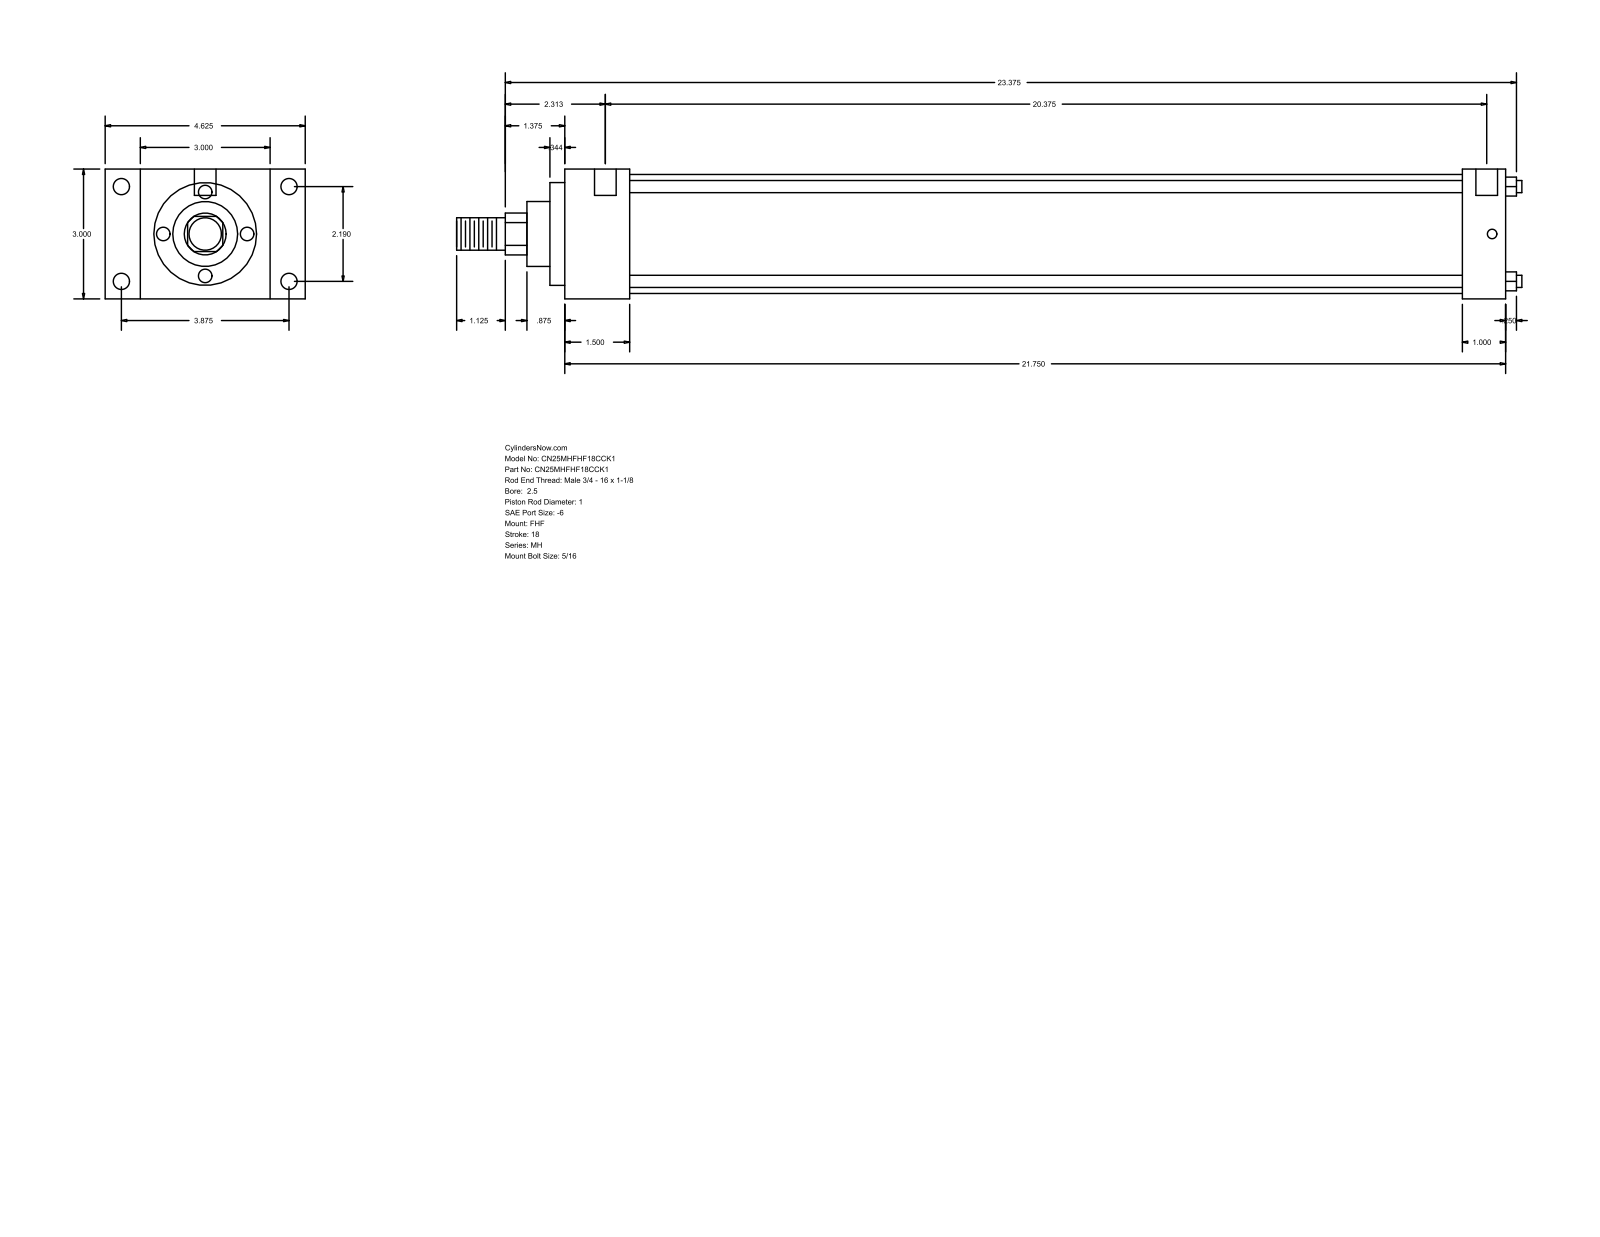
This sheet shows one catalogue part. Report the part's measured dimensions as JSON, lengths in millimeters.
{"part_name": "MH_FHF__0250_1", "step_written_by": "GSSL Pune (CONFIG_CONTROL_DESIGN)", "units": "millimeters", "bodies": {"solids": 0, "faces": 90, "planar": 61, "cylindrical": 29, "other": 0}, "overall_size": [625.48, 117.47, 76.2], "round_holes": [[5.56, 4], [9.53, 4], [12.7, 2]], "round_bosses_or_shafts": [[7.14, 4], [69.85, 1], [60.33, 1], [38.1, 1], [25.4, 1], [19.05, 1]], "partial_cylinders_radius": [[12.29, 1]], "face_to_face_distances": [76.2, 552.46, 38.11, 514.35, 20.64, 96.84, 117.48, 527.06, 488.95, 25.4], "hole_center_spacings": [55.62, 98.42, 113.05, 525.46, 3.18, 4.76, 517.52, 520.7]}
